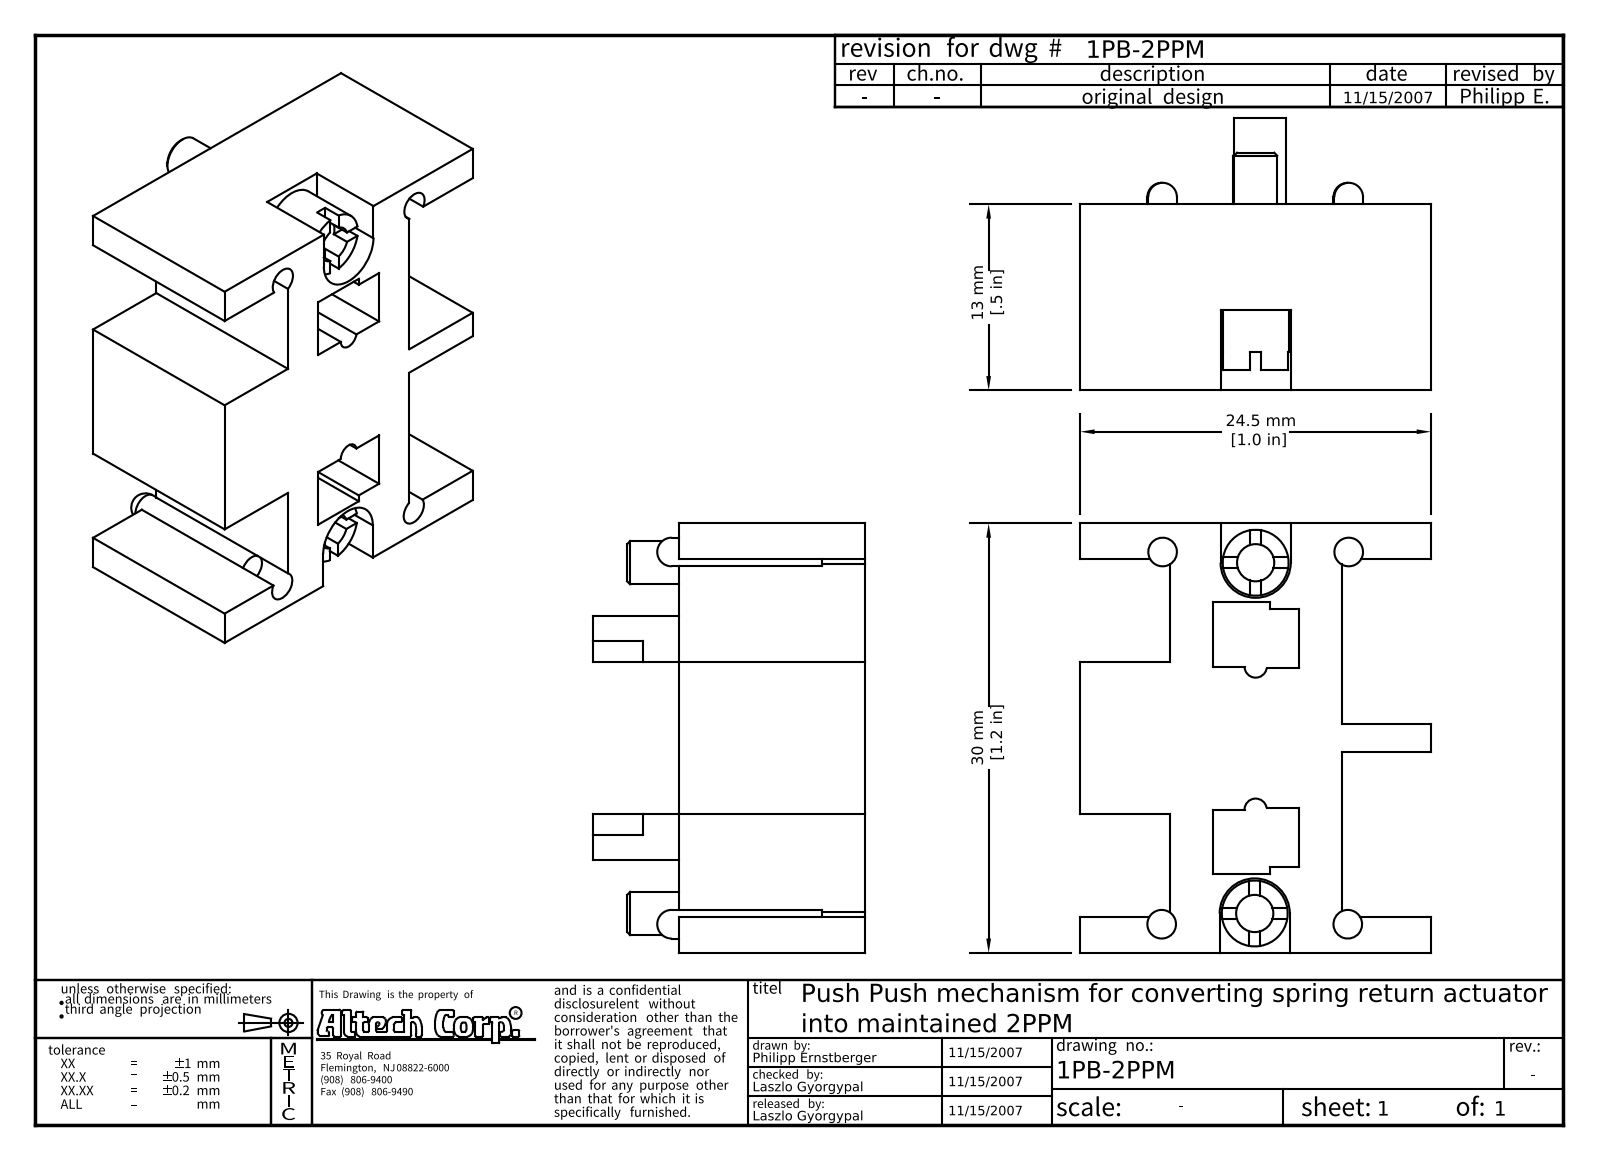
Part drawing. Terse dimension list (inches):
name: 2PPM; screw
written by: Autodesk Inventor 2008 (AUTOMOTIVE_DESIGN)
unit: in
bodies: 3 solids, 134 faces (89 planar, 23 cylindrical, 22 other)
size: 1.181 × 0.965 × 0.748
volume: 0.377 in³; area: 6.566 in²
holes: 4× ⌀0.079, 2× ⌀0.098, 2× ⌀0.102
bosses: 2× ⌀0.181, 2× ⌀0.118
rounds: 2× R0.096, 1× R0.031
face distances: 0.512, 0.719, 1.181, 0.246, 0.098, 1.083, 0.472, 0.382, 0.799, 0.283
hole spacings: 0.257, 0.512, 1.024, 1.026, 1.027, 0.965, 1.143, 1.146
